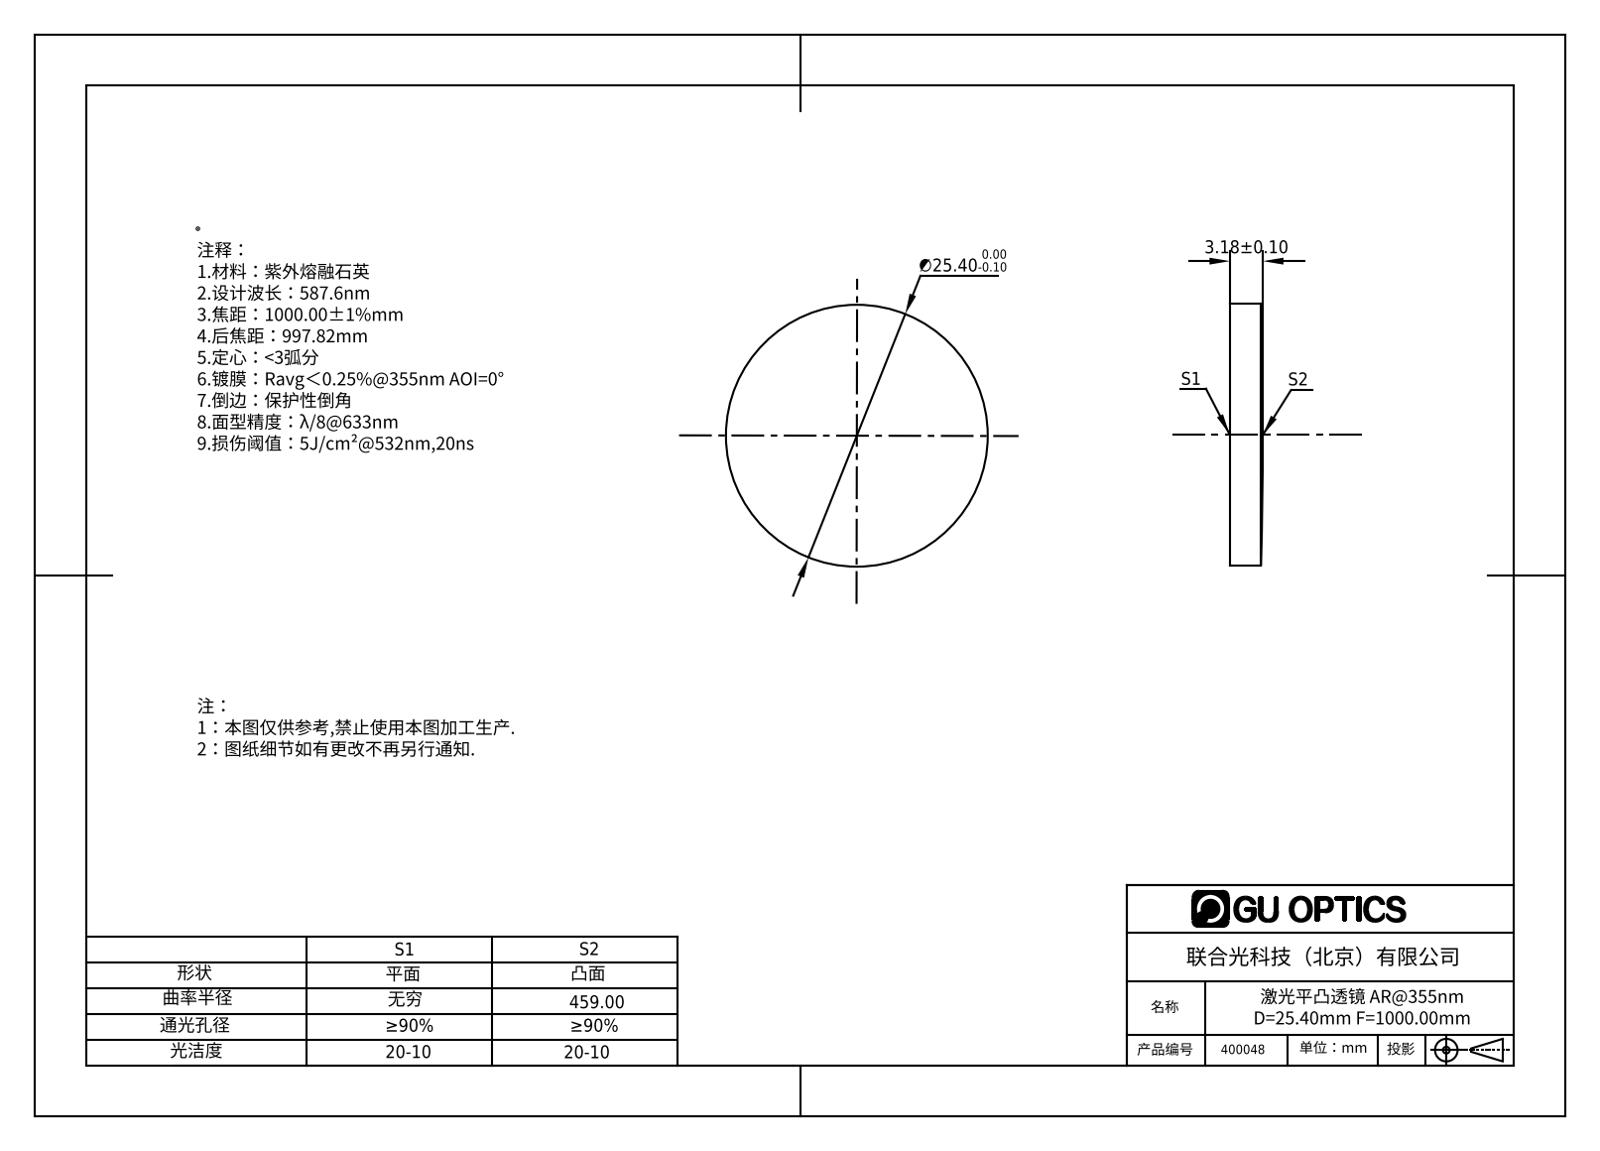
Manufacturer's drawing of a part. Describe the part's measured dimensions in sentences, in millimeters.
The part is named "400022". Its 3-D file was written by "SolidWorks 2016 (AUTOMOTIVE_DESIGN)". It is 1 solid with 5 faces: 1 planar, 2 cylindrical and 2 other. Overall it measures 25.4 by 25.4 by 3.18 millimeters. Its volume is 1 565 cubic millimeters and its surface area 1 253 square millimeters. Round bosses or shafts: 1 of diameter 25.4.
